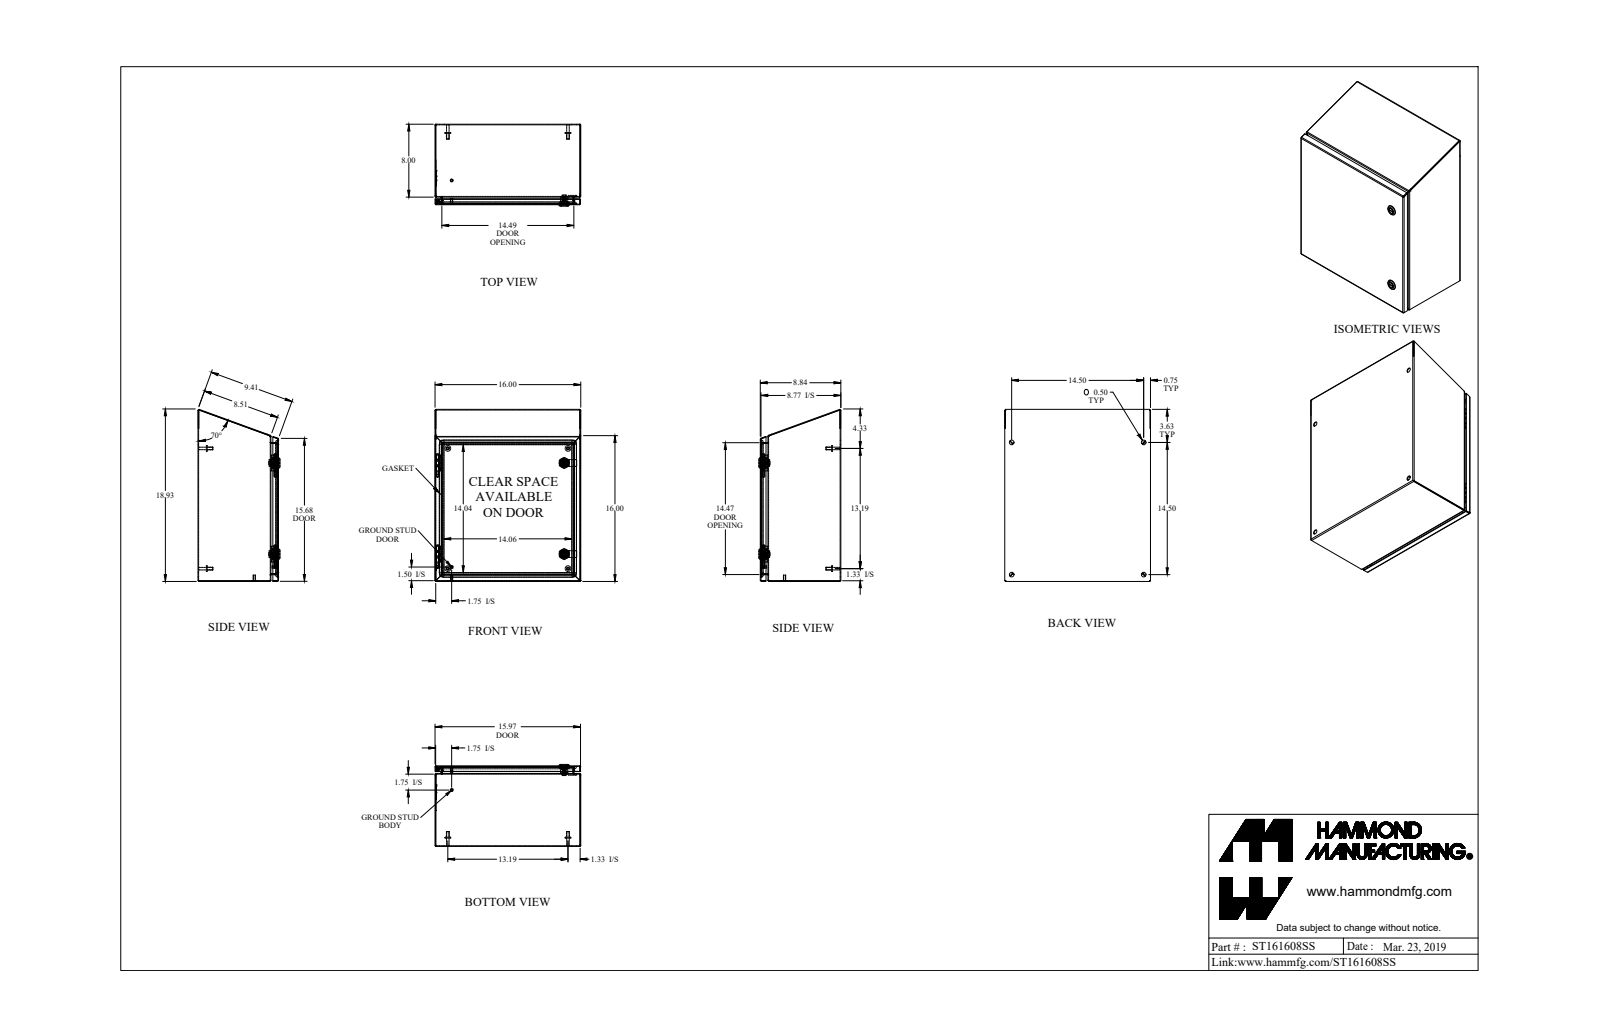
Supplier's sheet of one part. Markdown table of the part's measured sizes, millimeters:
| quantity | value |
| --- | --- |
| part name | ST161608SS |
| STEP written by | SolidWorks 2018 (AUTOMOTIVE_DESIGN) |
| units | millimeters |
| bodies | 27 solids, 777 faces (410 planar, 231 cylindrical, 136 other) |
| overall size | 479.6 × 406.4 × 228.5 |
| volume | 1 550 000 mm³ |
| surface area | 1 677 000 mm² |
| round holes (diameter × count) | 12.7 × 6, 5 × 2, 9.8 × 2, 16 × 2, 19.5 × 2, 4.4 × 1, 6.1 × 1, 6.1 × 1 |
| round bosses / shafts (diameter × count) | 15.9 × 6, 8 × 6, 7 × 4, 27.9 × 2, 19.9 × 2, 13.3 × 2, 6.4 × 2, 6 × 2 |
| partial cylindrical surfaces (radius × count) | 0.9 × 20, 2.7 × 20, 6.4 × 11, 0.2 × 4, 1.6 × 4, 3.2 × 4, 12.7 × 4, 7.8 × 2 |
| main face-to-face distances | 1.8, 222.6, 220.8, 404.6, 224.5, 402.7, 406.4, 201.4, 21.3, 23.1 |
| hole center spacings | 368.3, 63.3, 312.3, 345.8, 461.6, 520.9, 254 |
